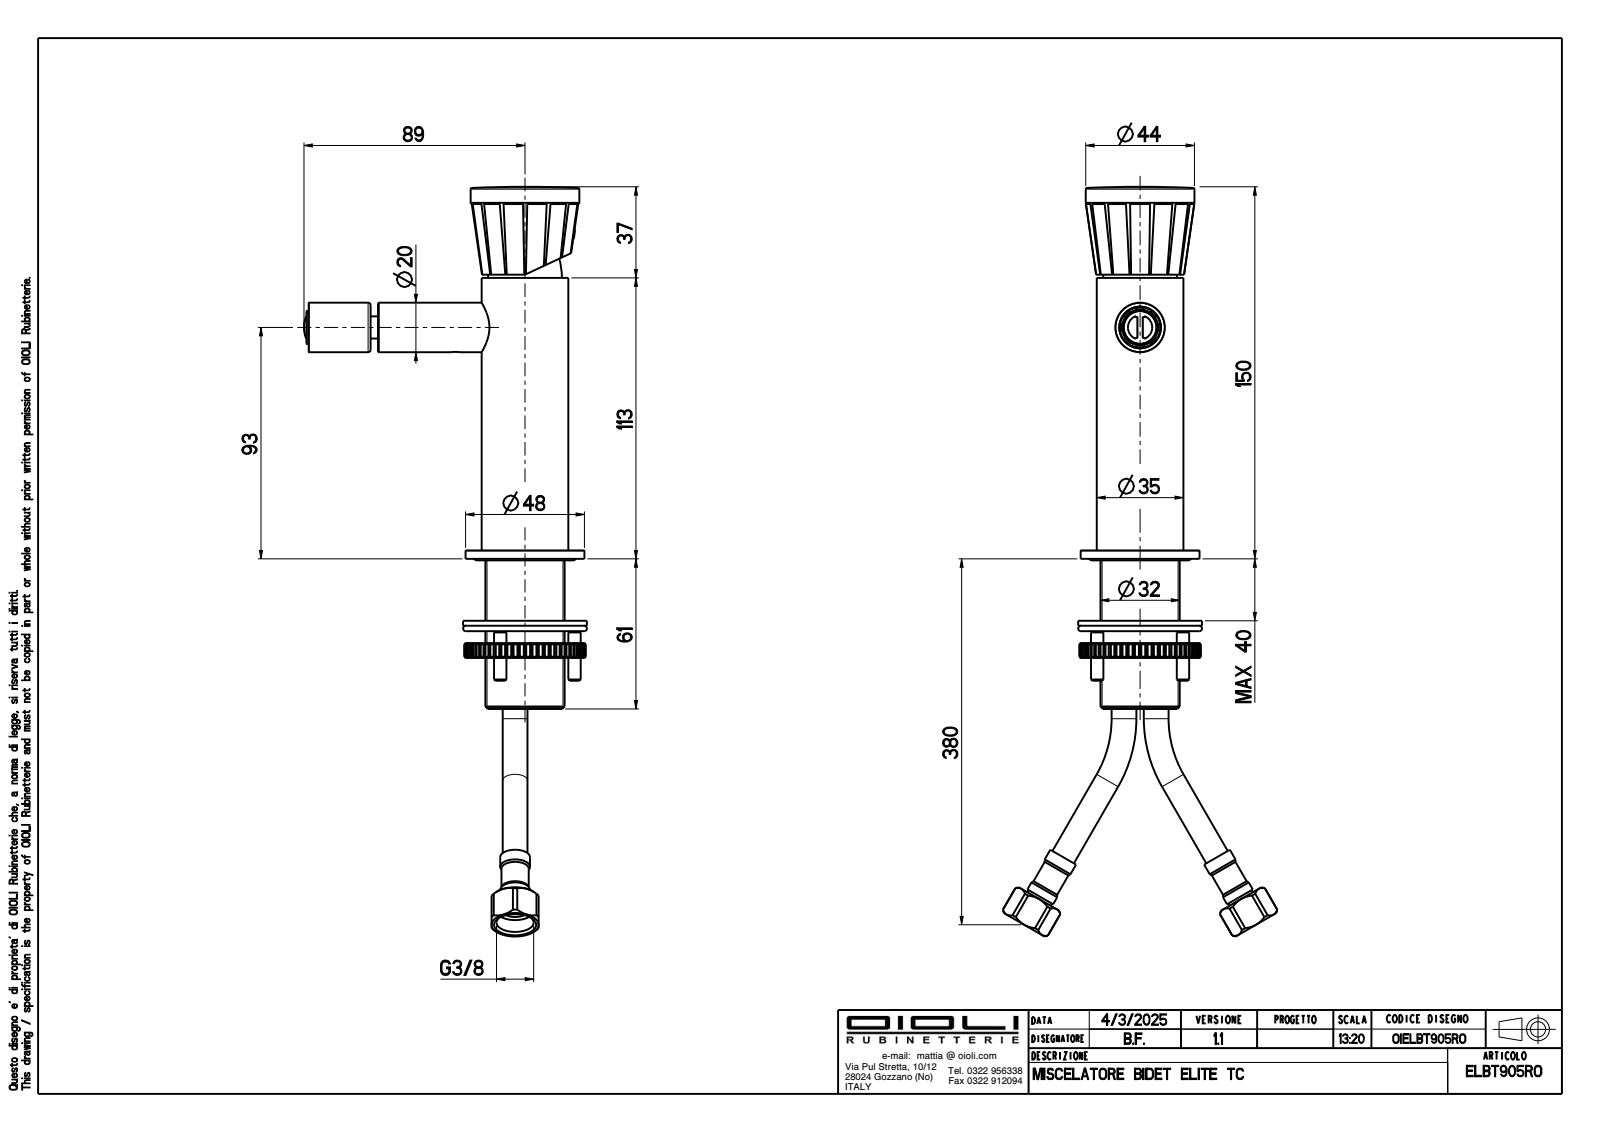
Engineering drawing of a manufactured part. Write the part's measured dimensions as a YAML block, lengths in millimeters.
part_name: "OIBR00322; OIBR00066; OIBR00381; OIVT00002 (+7 more)"
step_written_by: "CREO PARAMETRIC BY PTC INC, 2024493 (CONFIG_CONTROL_DESIGN)"
units: millimeters
bodies: {solids: 11, faces: 1044, planar: 590, cylindrical: 200, other: 254}
overall_size: [150.18, 113.26, 48]
volume: 80503
surface_area: 52943
round_holes:
  - {diameter: 3.2, count: 2}
  - {diameter: 5, count: 2}
  - {diameter: 7, count: 2}
  - {diameter: 9, count: 2}
  - {diameter: 3.3, count: 1}
  - {diameter: 4, count: 1}
  - {diameter: 4.2, count: 1}
  - {diameter: 5.3, count: 1}
  - {diameter: 6.5, count: 1}
  - {diameter: 9.5, count: 1}
  - {diameter: 11, count: 1}
  - {diameter: 14.55, count: 1}
round_bosses_or_shafts:
  - {diameter: 16.5, count: 2}
  - {diameter: 8, count: 2}
  - {diameter: 48, count: 1}
  - {diameter: 43.9, count: 1}
  - {diameter: 35.6, count: 1}
  - {diameter: 35, count: 1}
  - {diameter: 32, count: 1}
  - {diameter: 27, count: 1}
partial_cylinders:
  - {radius: 0.1, count: 14}
  - {radius: 0.9, count: 8}
  - {radius: 0.6, count: 4}
  - {radius: 0.45, count: 3}
  - {radius: 2.5, count: 1}
  - {radius: 3.25, count: 1}
  - {radius: 6.72, count: 1}
  - {radius: 7.46, count: 1}
face_to_face_distances: [143.8, 3.4, 147.2, 63.4, 60, 83.8, 28, 33.8, 113.4, 110]
hole_center_spacings: [1.9, 6.72, 7.63, 8.14, 8.94, 9.33, 11.27, 15.46]
